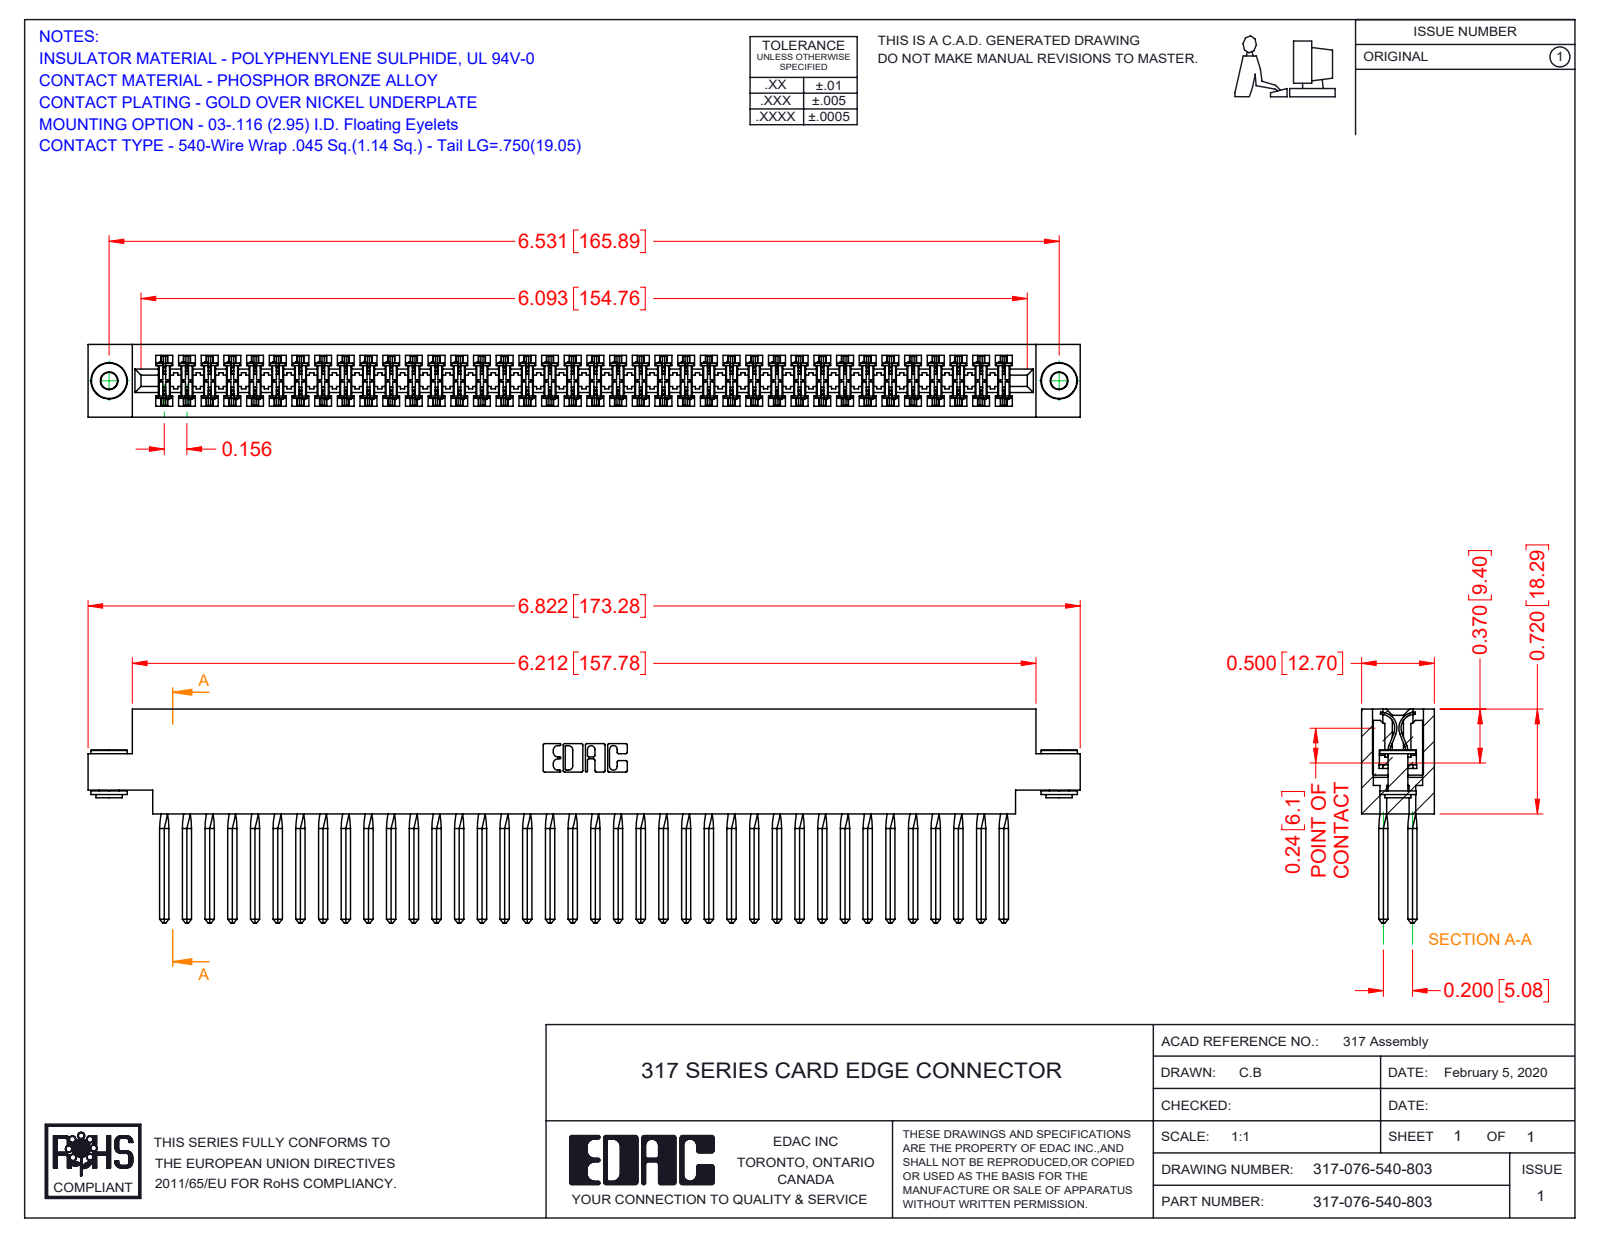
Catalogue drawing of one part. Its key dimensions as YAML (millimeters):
part_name: "345-250-002_345-250-002-102; 317 Part_.156 Dia - TH; 317-076-540-803; 317-290-001_540"
step_written_by: "SolidWorks 2016 (CONFIG_CONTROL_DESIGN)"
units: millimeters
bodies: {solids: 79, faces: 6904, planar: 5616, cylindrical: 976, other: 312}
overall_size: [173.3, 37.3, 12.7]
volume: 28970
surface_area: 43250
round_holes:
  - {diameter: 2.9, count: 2}
  - {diameter: 4, count: 2}
round_bosses_or_shafts:
  - {diameter: 6.4, count: 2}
  - {diameter: 4.6, count: 2}
  - {diameter: 3.5, count: 2}
partial_cylinders:
  - {radius: 0.4, count: 152}
  - {radius: 0.3, count: 22}
  - {radius: 0.2, count: 6}
  - {radius: 0.8, count: 6}
  - {radius: 0.7, count: 3}
  - {radius: 2.4, count: 2}
  - {radius: 2.5, count: 2}
  - {radius: 2.8, count: 2}
face_to_face_distances: [12.7, 1.9, 10.8, 8.9, 5, 2.4, 2.8, 5.1, 2.9, 3.3]
hole_center_spacings: [165.9]
